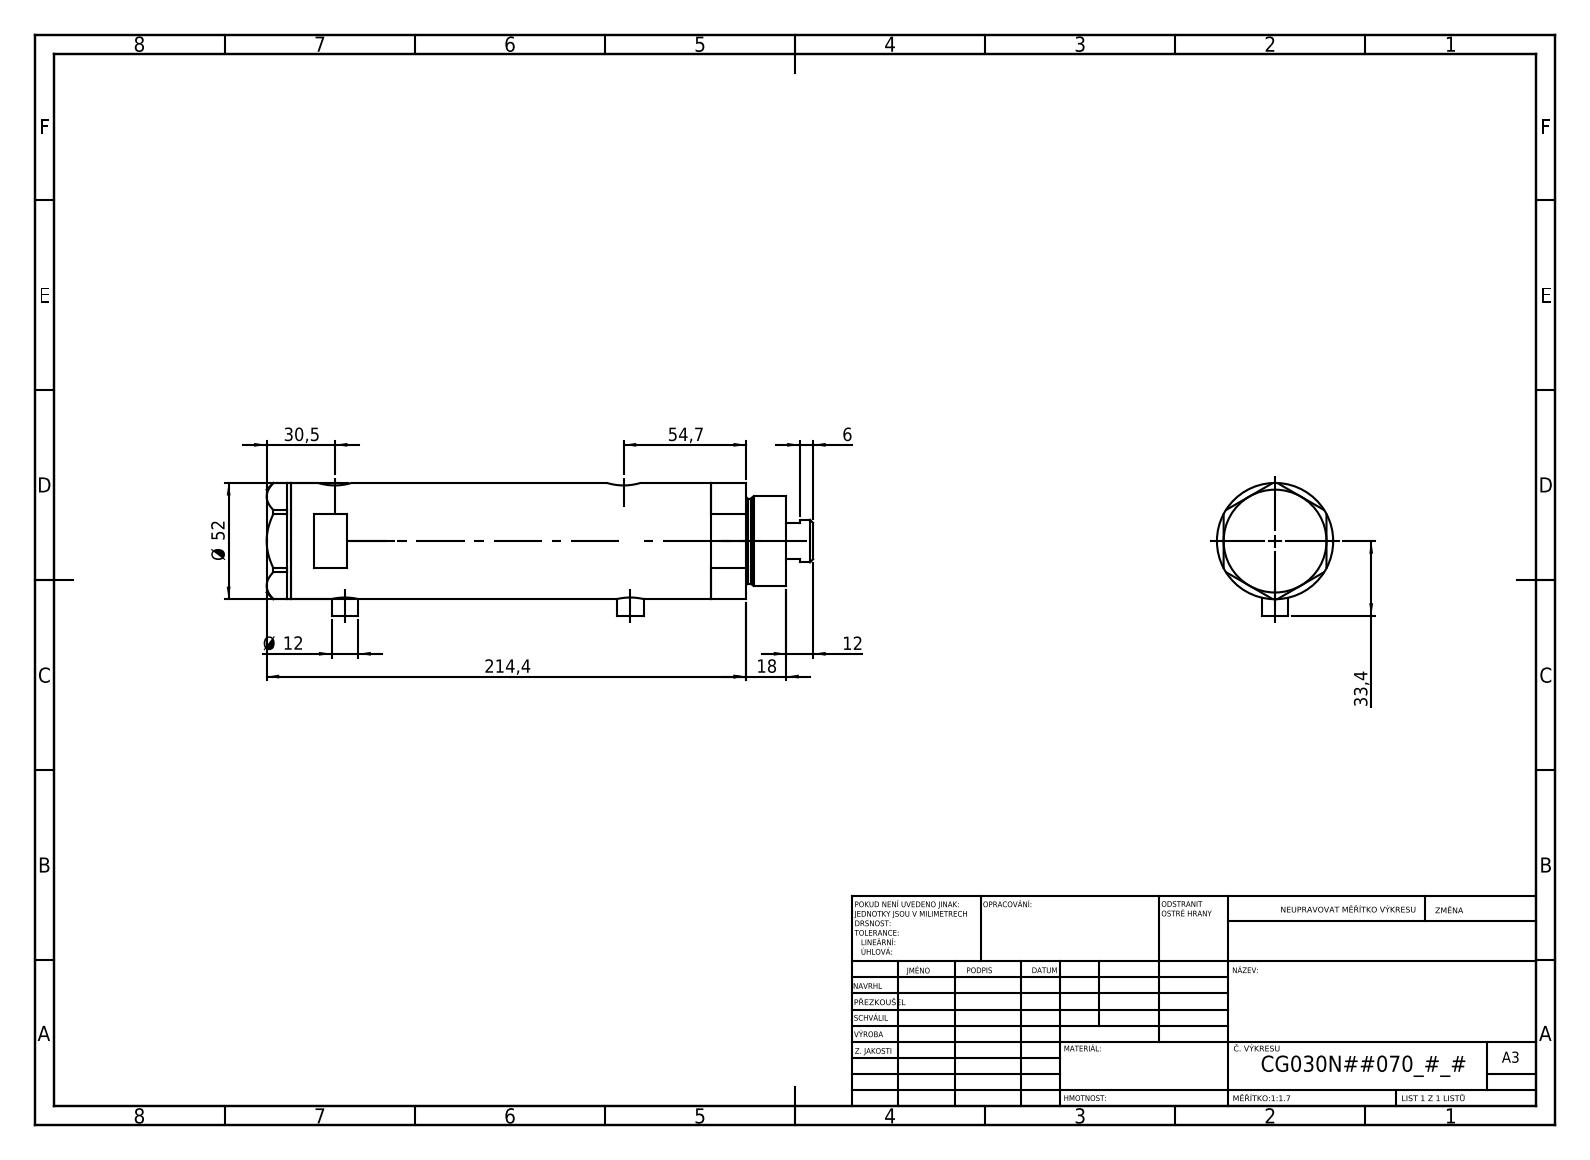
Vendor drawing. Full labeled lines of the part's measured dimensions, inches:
Part name (STEP PRODUCT): V270CG_BACK; V270CG_FRONT; V270CG_VC; V270CG_MIDDLE
STEP written by: SolidWorks 2019 (CONFIG_CONTROL_DESIGN)
Units: inches
Bodies: 4 solids, 134 faces (65 planar, 49 cylindrical, 20 other)
Overall size (bounding box): 9.622 × 2.339 × 2.047
Volume: 27.26 in³ · Surface area: 150.3 in²
Round holes (diameter × count): ⌀0.383 ×2, ⌀0.492 ×2, ⌀0.591 ×2, ⌀0.256 ×1, ⌀0.787 ×1, ⌀0.846 ×1, ⌀1.181 ×1, ⌀1.299 ×1, ⌀1.732 ×1
Round bosses / shafts (diameter × count): ⌀0.472 ×2, ⌀2.047 ×1, ⌀1.575 ×1, ⌀1.496 ×1, ⌀0.748 ×1
Main face-to-face distances: 5.965, 0.937, 5.028, 0.433, 1.37, 6.398, 1.811, 7.831, 7.398, 6.461
Hole centre spacings: 0.114, 0.177, 4.909, 5.024, 5.087, 5.201
